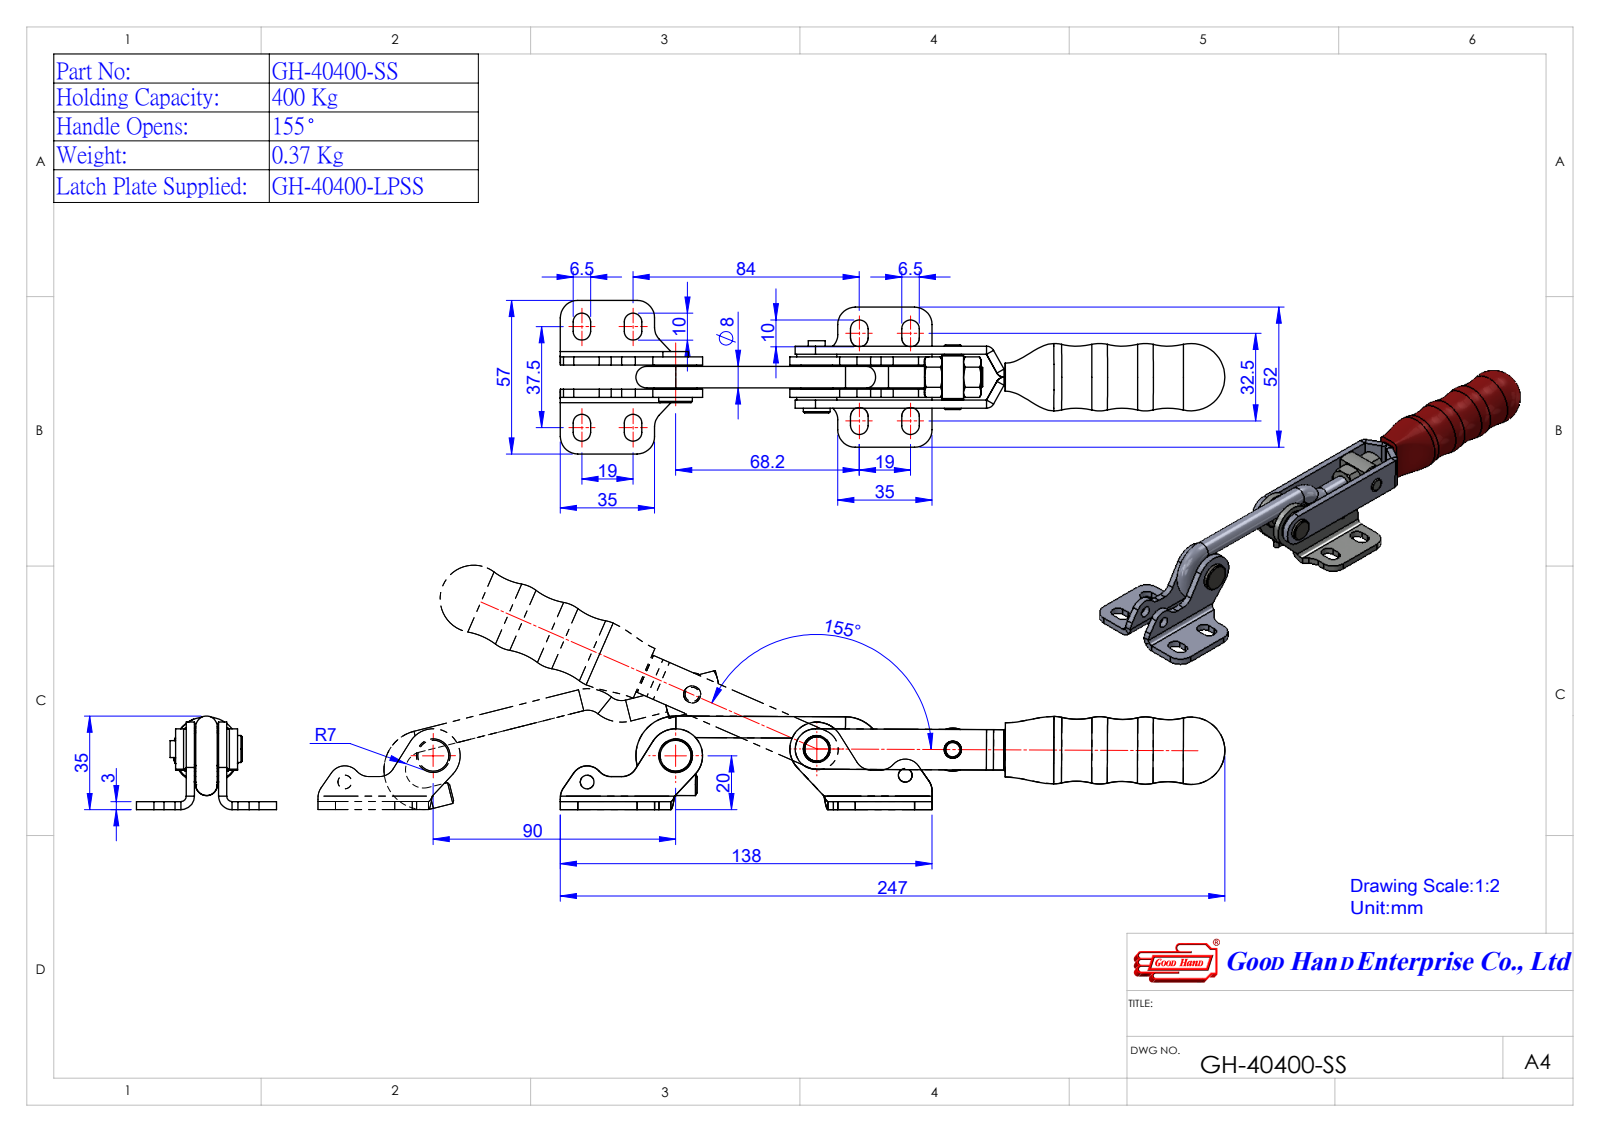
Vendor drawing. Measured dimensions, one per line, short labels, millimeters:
name: GH-40400-SS(簡化); 44040044-1^GH-40400(簡化); Group5^GH-40400(簡化); Group2^GH-40400(簡化) (+2 more)
written by: SolidWorks 2016 (AUTOMOTIVE_DESIGN)
unit: mm
bodies: 5 solids, 336 faces (131 planar, 117 cylindrical, 88 other)
size: 246.7 × 57 × 34.75
volume: 71 932 mm³; area: 33 889 mm²
holes: 2× ⌀5.5, 1× ⌀8
bosses: 3× ⌀8, 1× ⌀16, 1× ⌀14.9, 1× ⌀12, 1× ⌀10, 1× ⌀9.5, 1× ⌀6.3
rounds: 16× R3.25, 10× R6, 10× R6.5, 4× R3.01, 2× R2, 2× R5, 2× R10, 1× R7.5
face distances: 3, 4, 16, 13, 1, 12, 19, 20, 7, 15
hole spacings: 50.5
